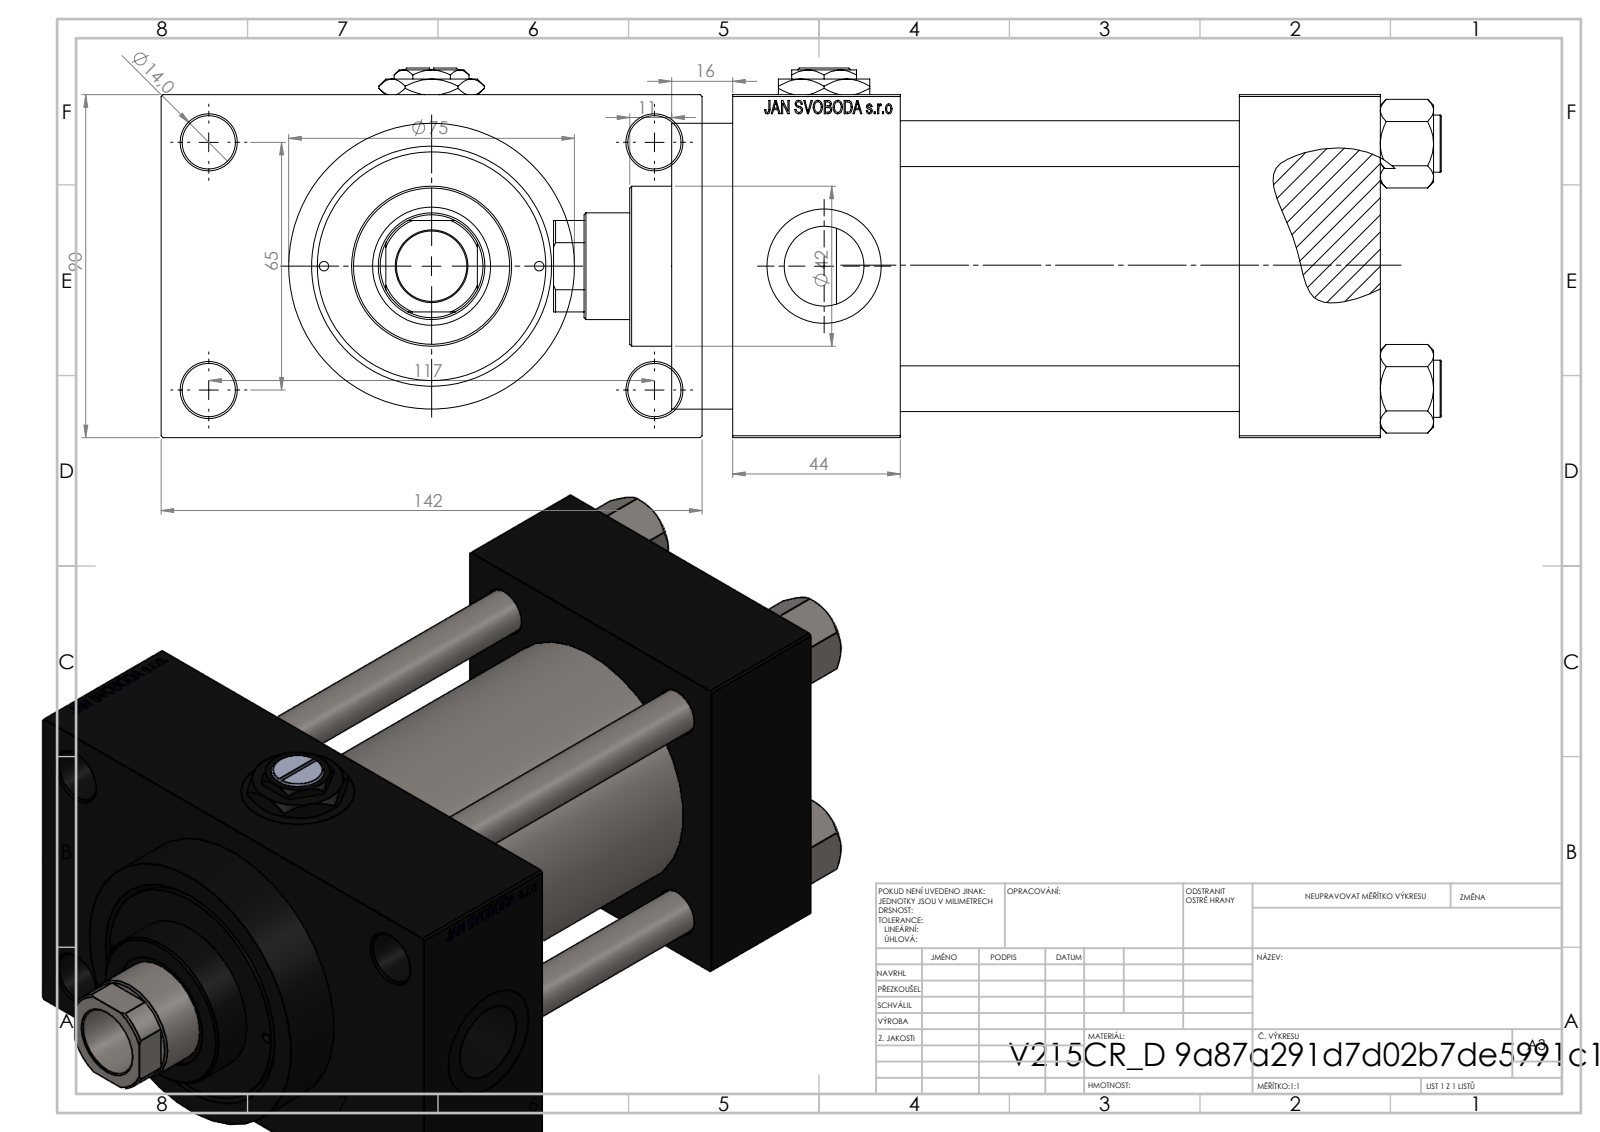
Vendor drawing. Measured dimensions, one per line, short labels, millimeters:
name: NUT_M5_D; V215CR_D_Body; V215CR_VCP_D; V215CR_D_TYCINKA (+2 more)
written by: SolidWorks 2019 (CONFIG_CONTROL_DESIGN)
unit: mm
bodies: 12 solids, 1159 faces (523 planar, 96 cylindrical, 540 other)
size: 233 × 142 × 97
volume: 1 144 000 mm³; area: 221 689 mm²
holes: 4× ⌀12, 4× ⌀14, 3× ⌀20.96, 3× ⌀30, 2× ⌀2.5, 2× ⌀7, 1× ⌀18.5, 1× ⌀28, 1× ⌀31, 1× ⌀50, 1× ⌀60, 1× ⌀63
bosses: 4× ⌀15, 1× ⌀75, 1× ⌀69, 1× ⌀42
rounds: 1× R13.5
face distances: 90, 89, 37, 126, 133, 170, 44, 116, 26, 142
hole spacings: 26.35, 32.39, 44.4, 45.47, 64.3, 66.92, 68.42, 69.81
